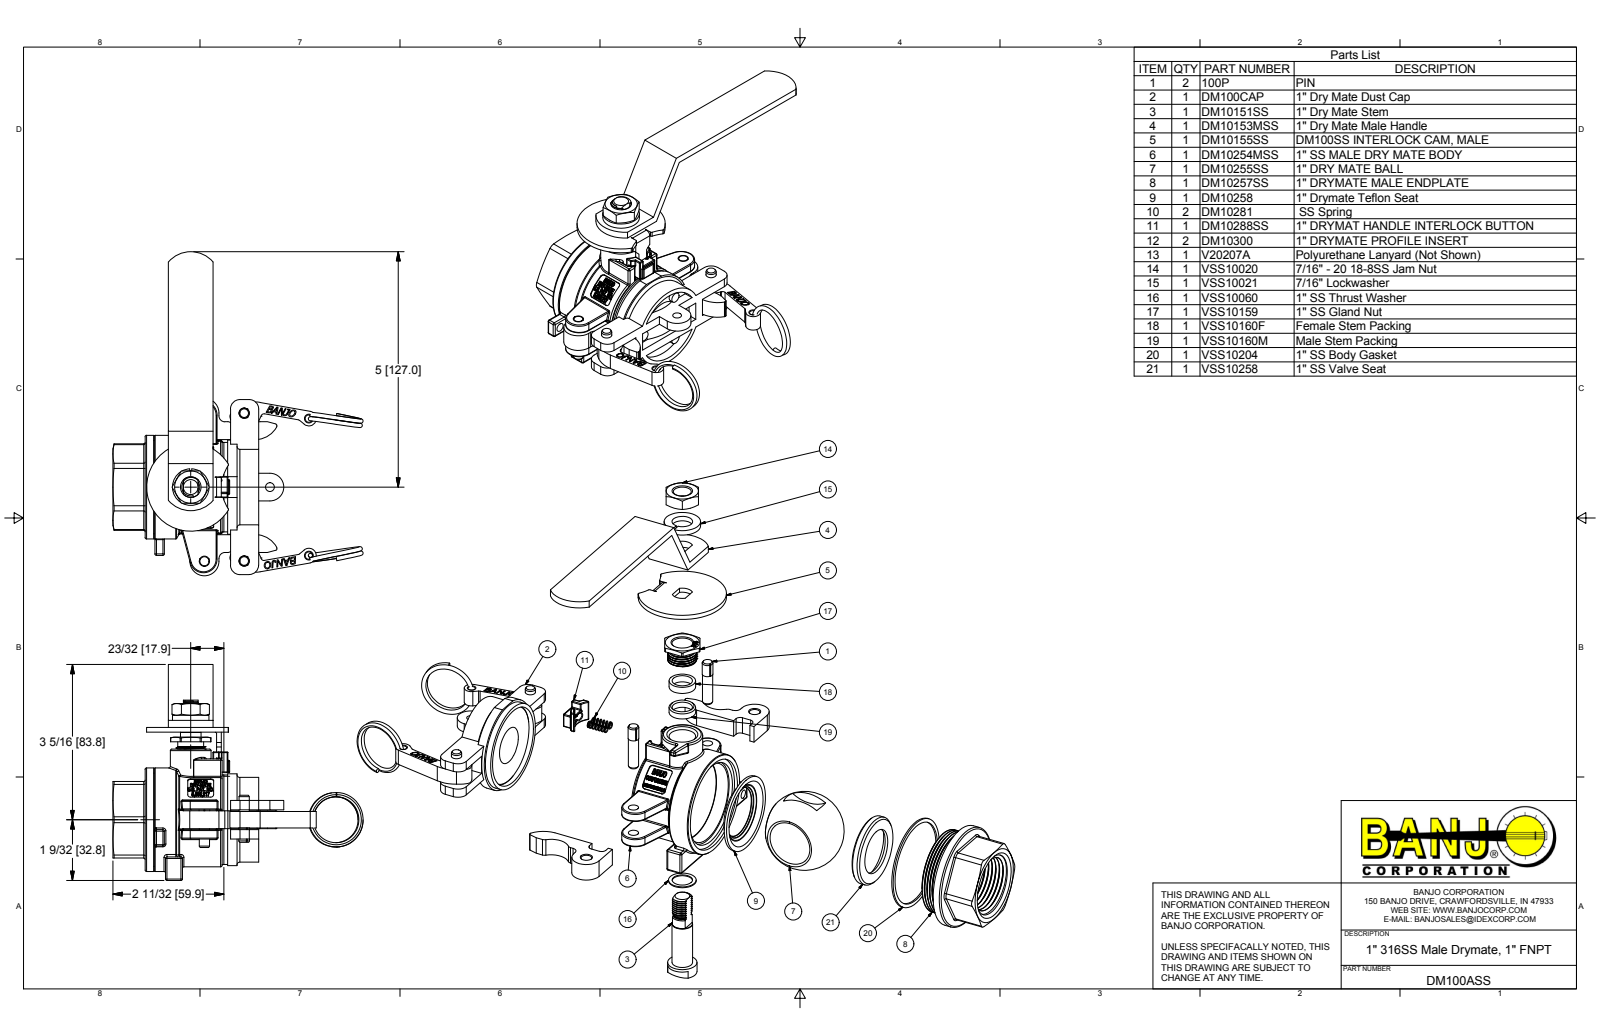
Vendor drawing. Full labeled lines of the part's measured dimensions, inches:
Part name (STEP PRODUCT): DM10254MSSX; DM10254MSS; 100P; DM10312 (+8 more)
STEP written by: Autodesk Inventor 2016 (AUTOMOTIVE_DESIGN)
Units: inches
Bodies: 34 solids, 2322 faces (874 planar, 490 cylindrical, 958 other)
Overall size (bounding box): 6.885 × 5.316 × 4.588
Volume: 10.22 in³ · Surface area: 155.4 in²
Round holes (diameter × count): ⌀0.125 ×3, ⌀0.156 ×2, ⌀0.218 ×2, ⌀0.219 ×2, ⌀0.225 ×2, ⌀0.228 ×2, ⌀0.187 ×1, ⌀0.188 ×1, ⌀0.383 ×1, ⌀0.432 ×1, ⌀0.434 ×1, ⌀0.438 ×1
Round bosses / shafts (diameter × count): ⌀0.227 ×4, ⌀0.217 ×4, ⌀0.22 ×3, ⌀0.01 ×2, ⌀2.2 ×1, ⌀2 ×1, ⌀1.98 ×1, ⌀1.96 ×1
Partial cylindrical surfaces — rounded edges, fillets, slot ends (radius × count): R0.031 ×55, R0.016 ×50, R0.02 ×28, R0.03 ×21, R0.063 ×10, R0.125 ×8, R0.1 ×5, R0.09 ×4
Main face-to-face distances: 0.15, 0.2, 1.188, 0.62, 0.1, 1.338, 1.55, 0.22, 0.6, 0.02
Hole centre spacings: 0.621, 1.076, 0.845, 1.381, 1.601, 1.662, 1.675, 1.937
